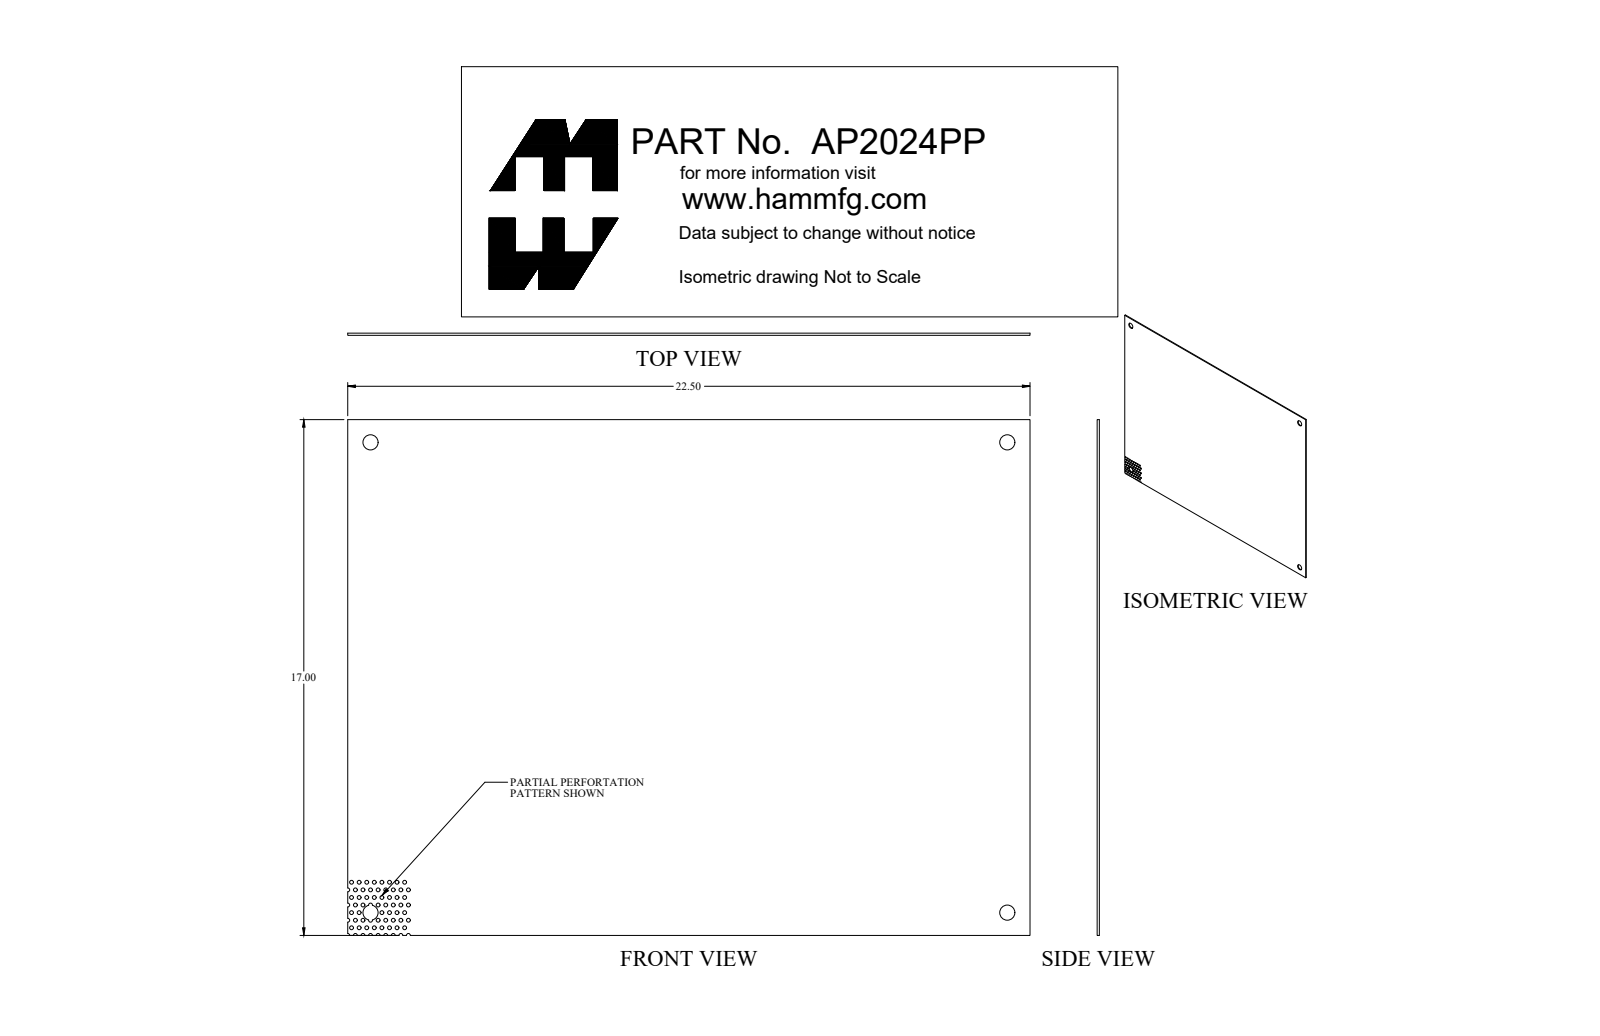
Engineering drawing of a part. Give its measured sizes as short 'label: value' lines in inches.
name: AP2024PP_Default
written by: SolidWorks 2019 (CONFIG_CONTROL_DESIGN)
unit: in
bodies: 1 solid, 152 faces (17 planar, 135 cylindrical, 0 other)
size: 22.5 × 17 × 0.072
volume: 27.43 in³; area: 769.7 in²
holes: 52× ⌀0.125, 4× ⌀0.5
rounds: 14× R0.062
face distances: 0.072, 17, 22.5
hole spacings: 0.5, 0.25, 0.559, 0.28, 0.279, 0.707, 0.75, 0.902
